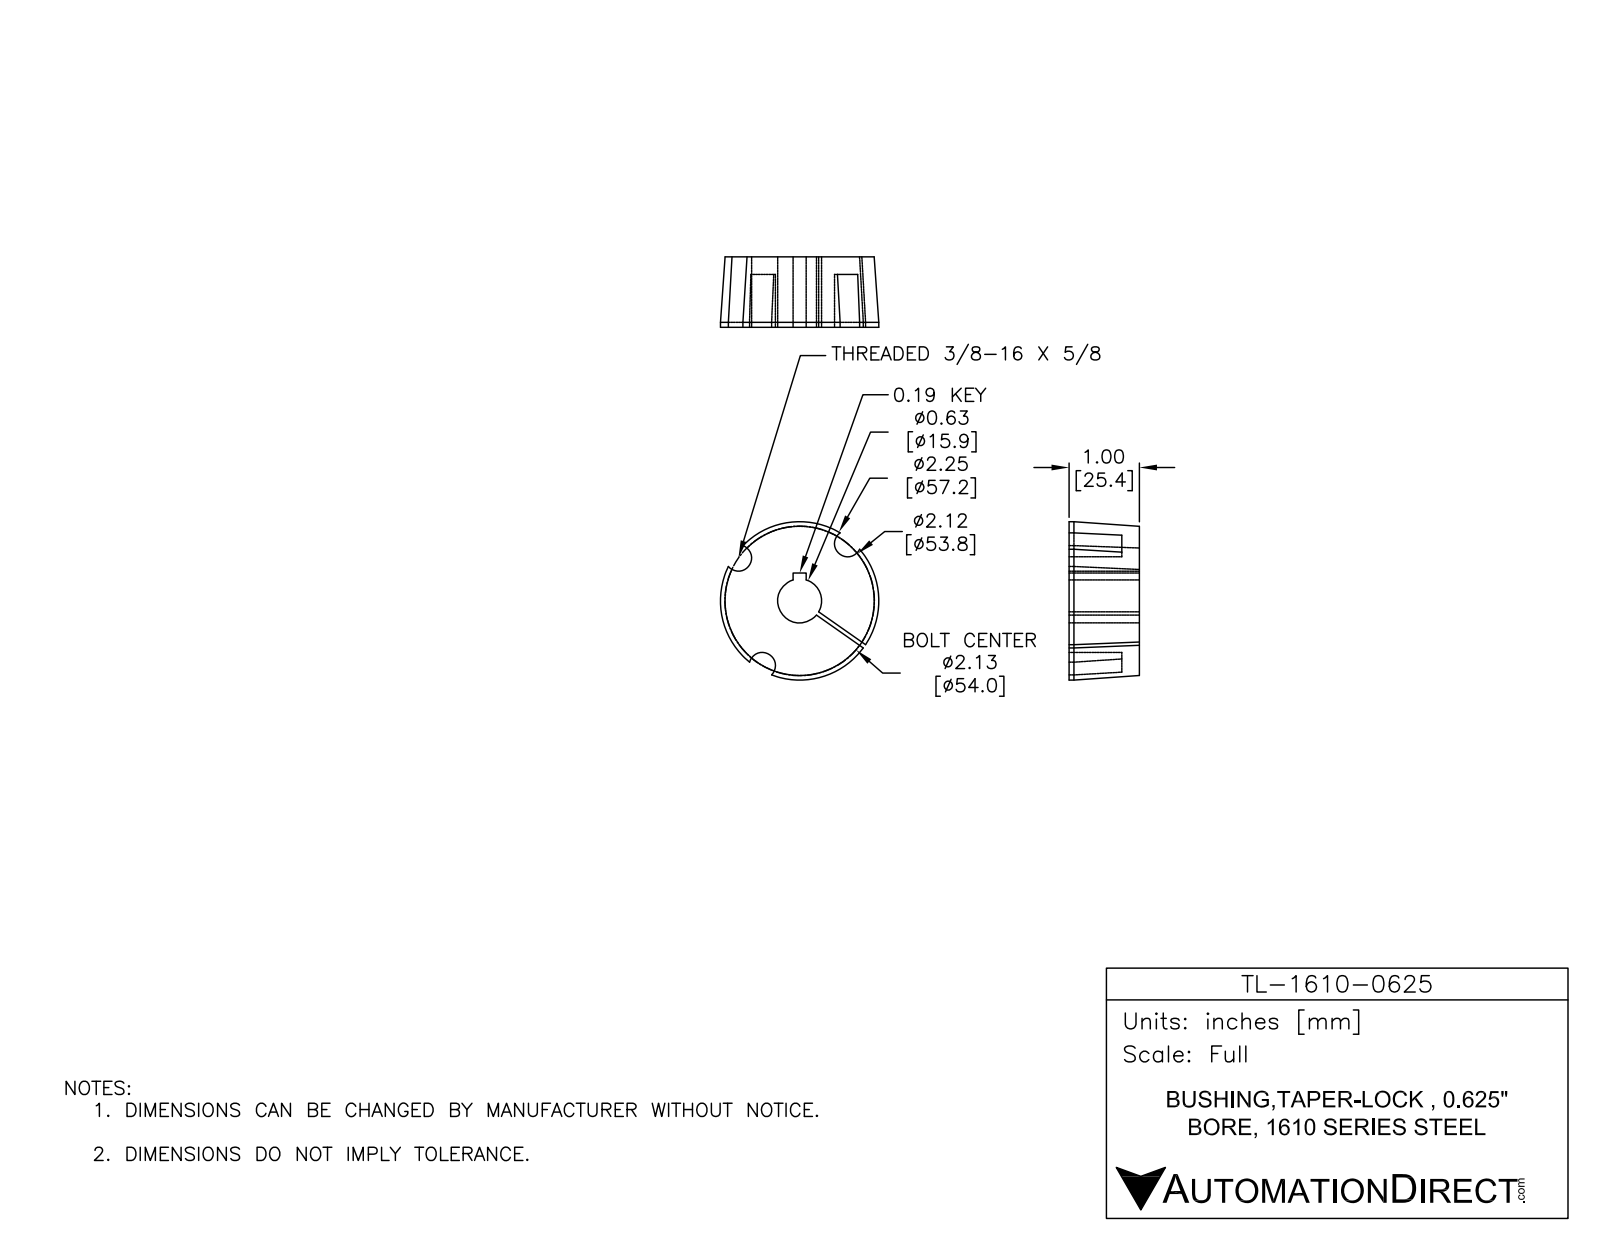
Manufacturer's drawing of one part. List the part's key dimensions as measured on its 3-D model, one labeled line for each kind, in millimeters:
Part name (STEP PRODUCT): TL-1610-0625
STEP written by: SolidWorks 2014 (AUTOMOTIVE_DESIGN)
Units: millimetres
Bodies: 1 solid, 25 faces (9 planar, 13 cylindrical, 3 other)
Overall size (bounding box): 57.2 × 57.2 × 25.4
Volume: 52 960 mm³ · Surface area: 11 450 mm²
Round holes (diameter × count): ⌀15.9 ×1
Round bosses / shafts (diameter × count): ⌀57.2 ×1
Partial cylindrical surfaces — rounded edges, fillets, slot ends (radius × count): R4.8 ×3
Main face-to-face distances: 25.4, 1.4, 6.4, 19.1, 4.7
